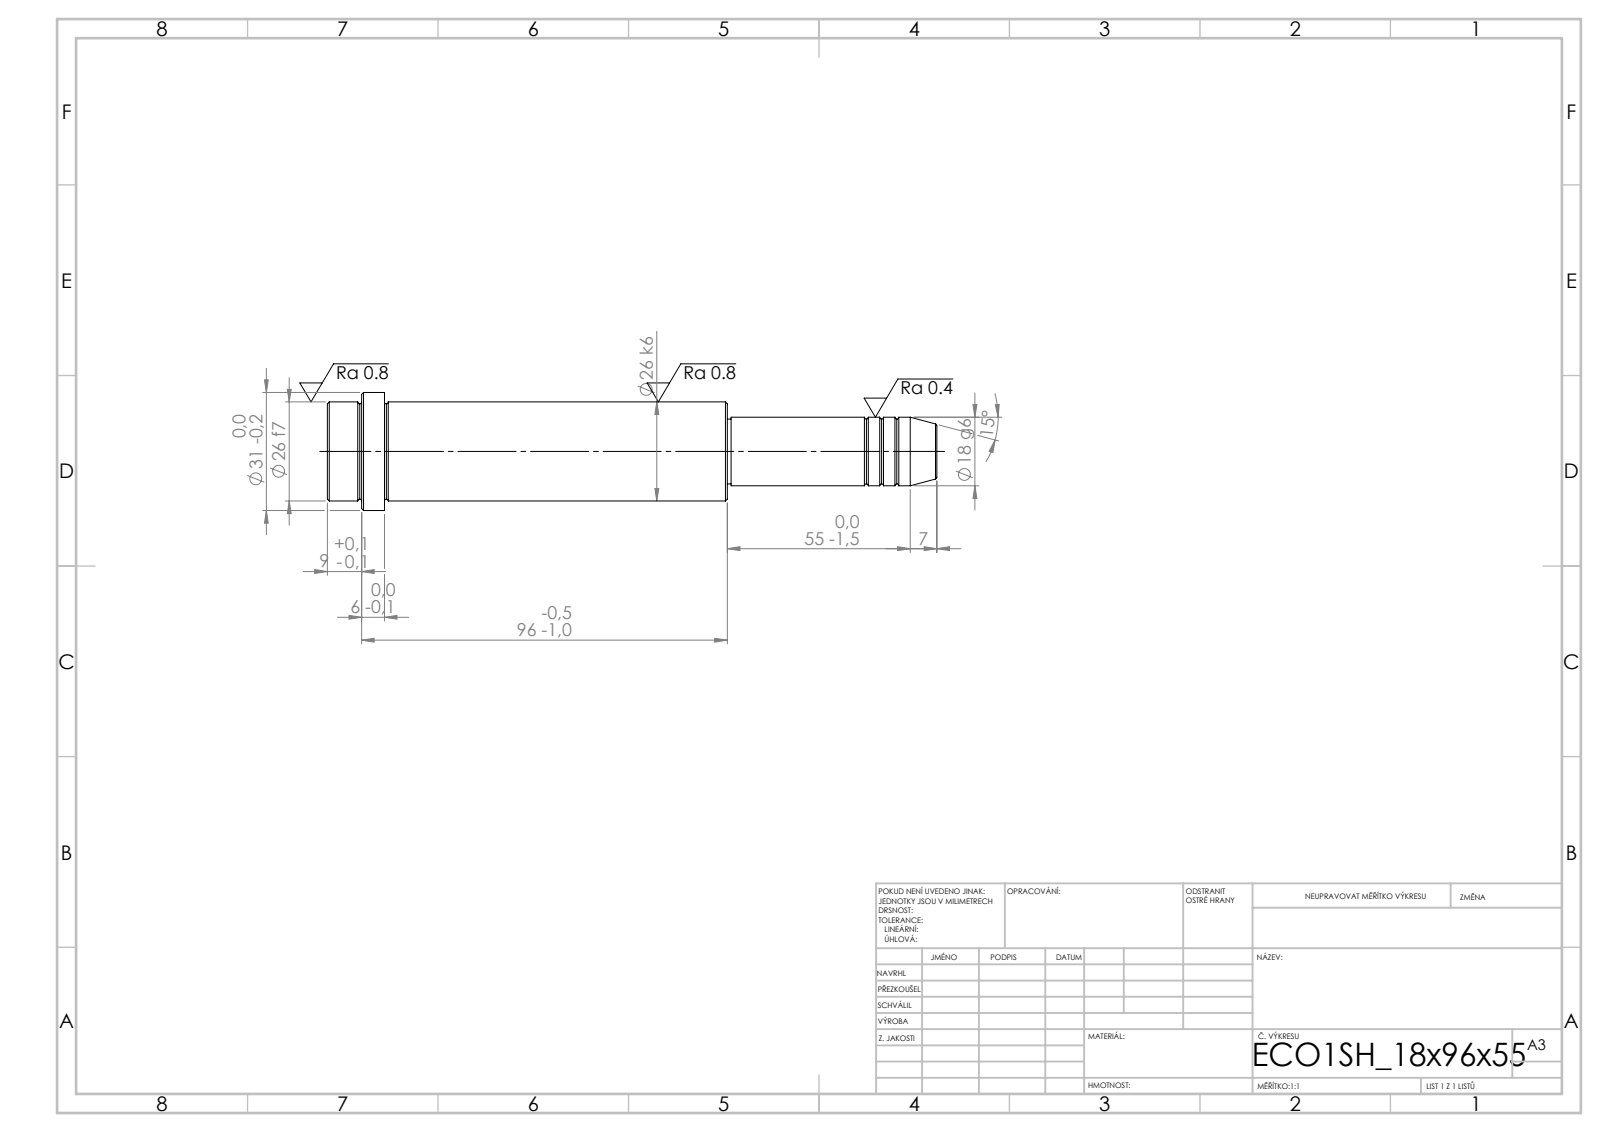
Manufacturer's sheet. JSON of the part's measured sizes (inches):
{"step_written_by": "SolidWorks 2019 (CONFIG_CONTROL_DESIGN)", "units": "inches", "bodies": {"solids": 1, "faces": 52, "planar": 6, "cylindrical": 16, "other": 30}, "overall_size": [6.299, 1.22, 1.22], "volume_in3": 4.305, "surface_area_in2": 20.63, "round_bosses_or_shafts": [[1.22, 1], [1.024, 1], [0.709, 1], [0.669, 1]], "face_to_face_distances": [4.134, 3.543, 0.591, 3.78, 0.236, 0.354, 2.165, 5.709, 5.945, 6.299]}
